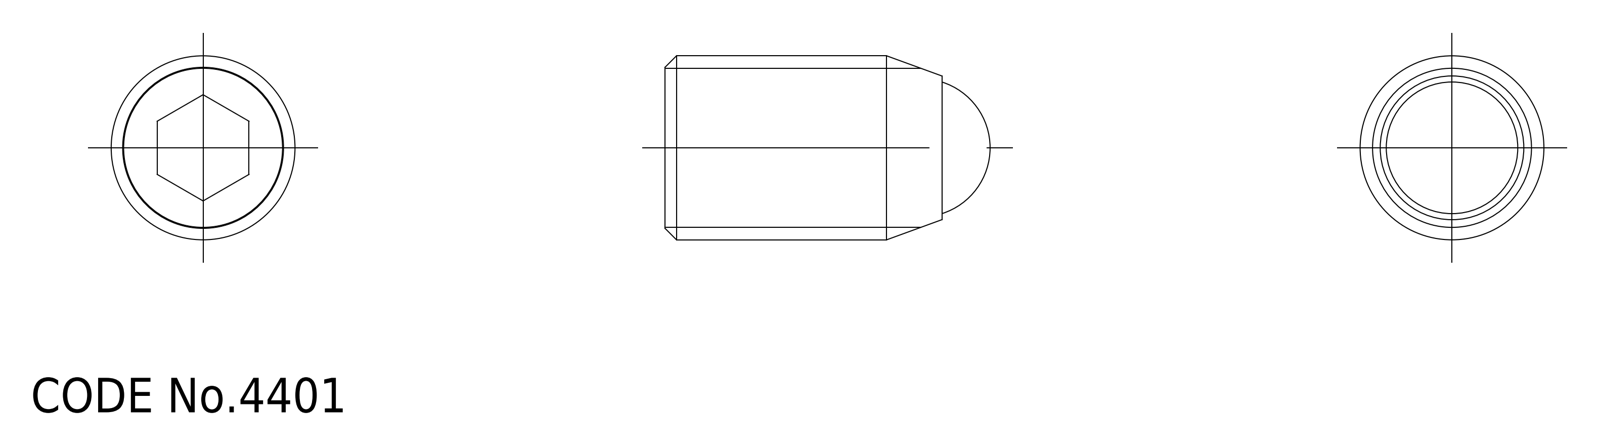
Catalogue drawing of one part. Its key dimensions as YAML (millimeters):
part_name: "ball; SCS_M16_25_R_16621_36"
step_written_by: "CADfix (AUTOMOTIVE_DESIGN)"
units: millimeters
bodies: {solids: 2, faces: 20, planar: 0, cylindrical: 0, other: 20}
overall_size: [28.3, 16, 16]
volume: 3889
surface_area: 2603
